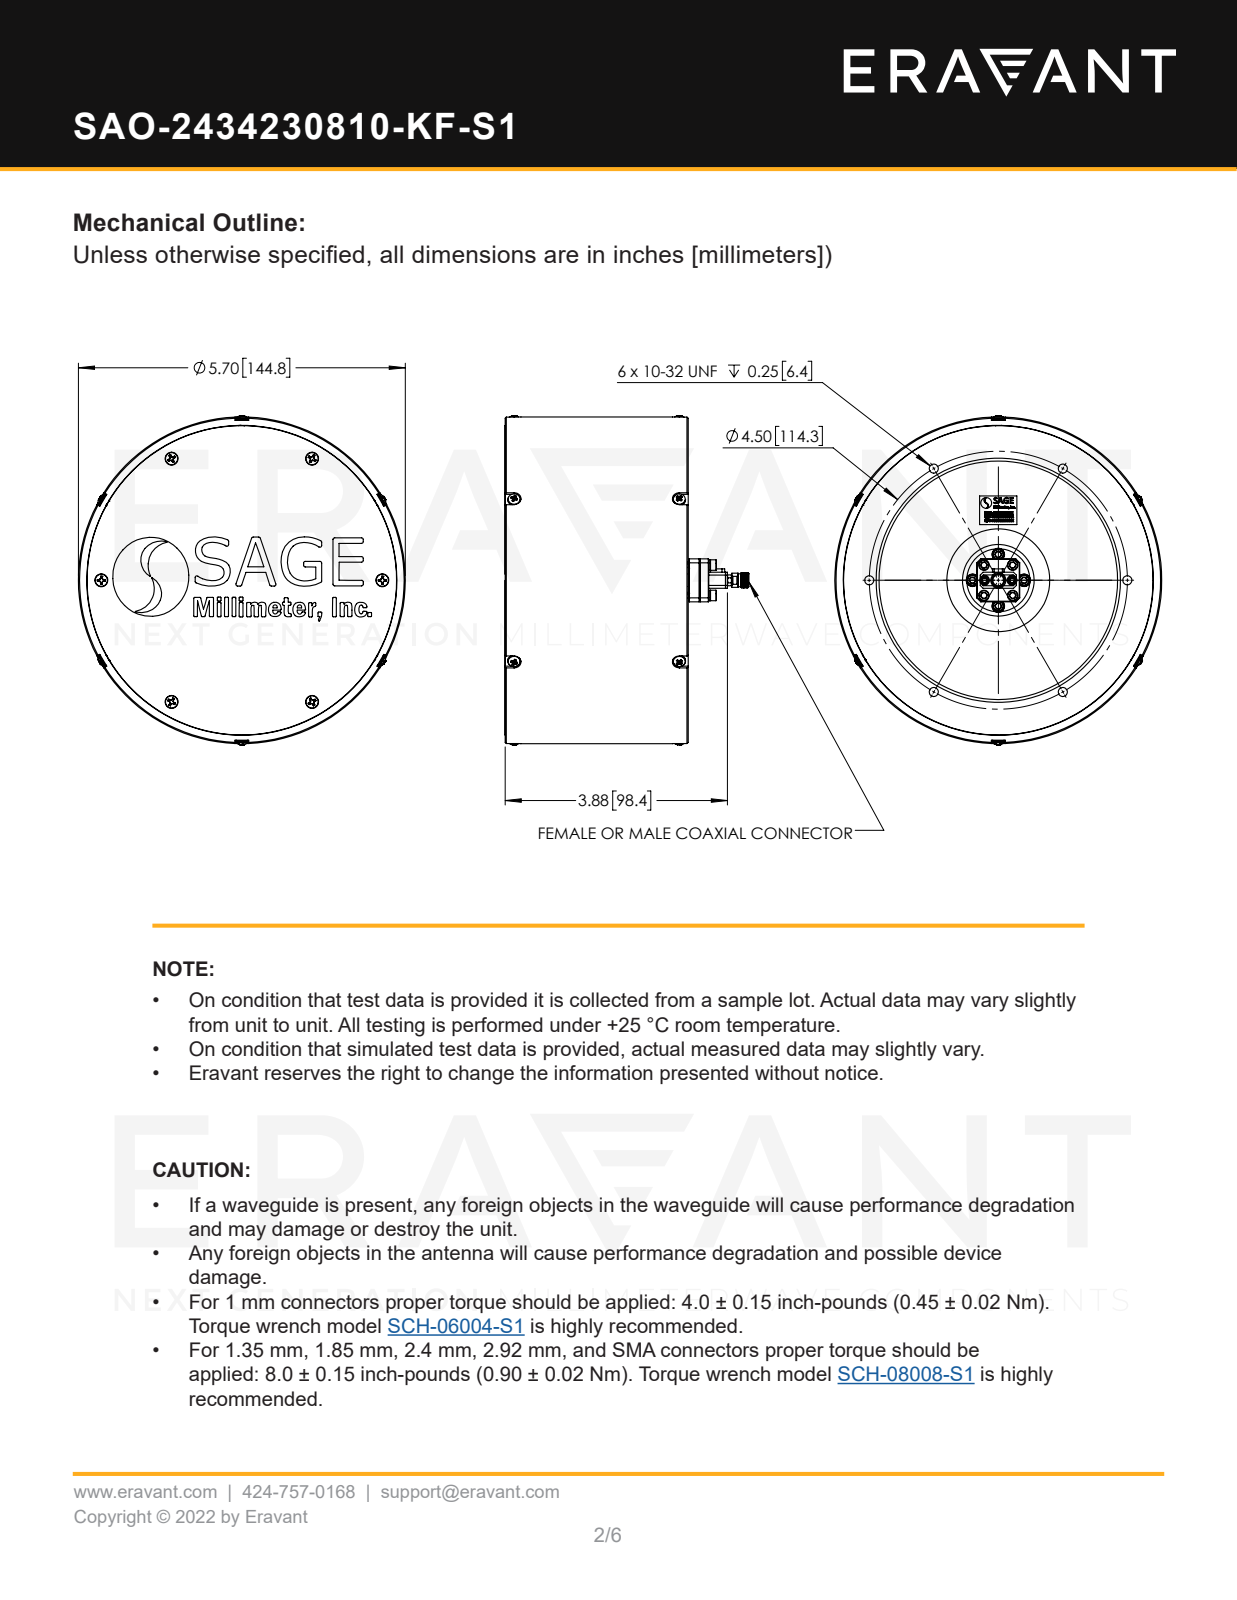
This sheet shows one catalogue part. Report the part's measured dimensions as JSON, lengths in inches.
{"part_name": "SAO-2734030810-KF-S1,defeatured", "step_written_by": "SolidWorks 2016 (CONFIG_CONTROL_DESIGN)", "units": "inches", "bodies": {"solids": 12, "faces": 2951, "planar": 1190, "cylindrical": 1169, "other": 592}, "overall_size": [5.734, 5.7, 4.384], "volume_in3": 71.66, "surface_area_in2": 129, "round_holes": [[0.129, 16], [0.159, 6], [0.089, 4], [0.116, 4], [0.12, 4], [0.219, 4], [0.033, 2], [0.07, 2], [0.09, 2], [0.102, 2], [0.19, 1], [0.21, 1]], "round_bosses_or_shafts": [[0.112, 12], [0.219, 10], [0.183, 8], [0.08, 6], [0.21, 4], [0.18, 4], [0.07, 4], [0.172, 2]], "partial_cylinders_radius": [[0.015, 84], [0.005, 28], [0.03, 24], [0.12, 10], [0.04, 8], [0.056, 8], [0.031, 2], [0.076, 1]], "face_to_face_distances": [3.194, 3.159, 0.035, 3.19, 0.031, 1.05, 2.109, 2.14, 2.144, 0.25], "hole_center_spacings": [2.45, 2.356, 2.88, 4.072, 2.25, 0.2, 4.7, 2.578]}
